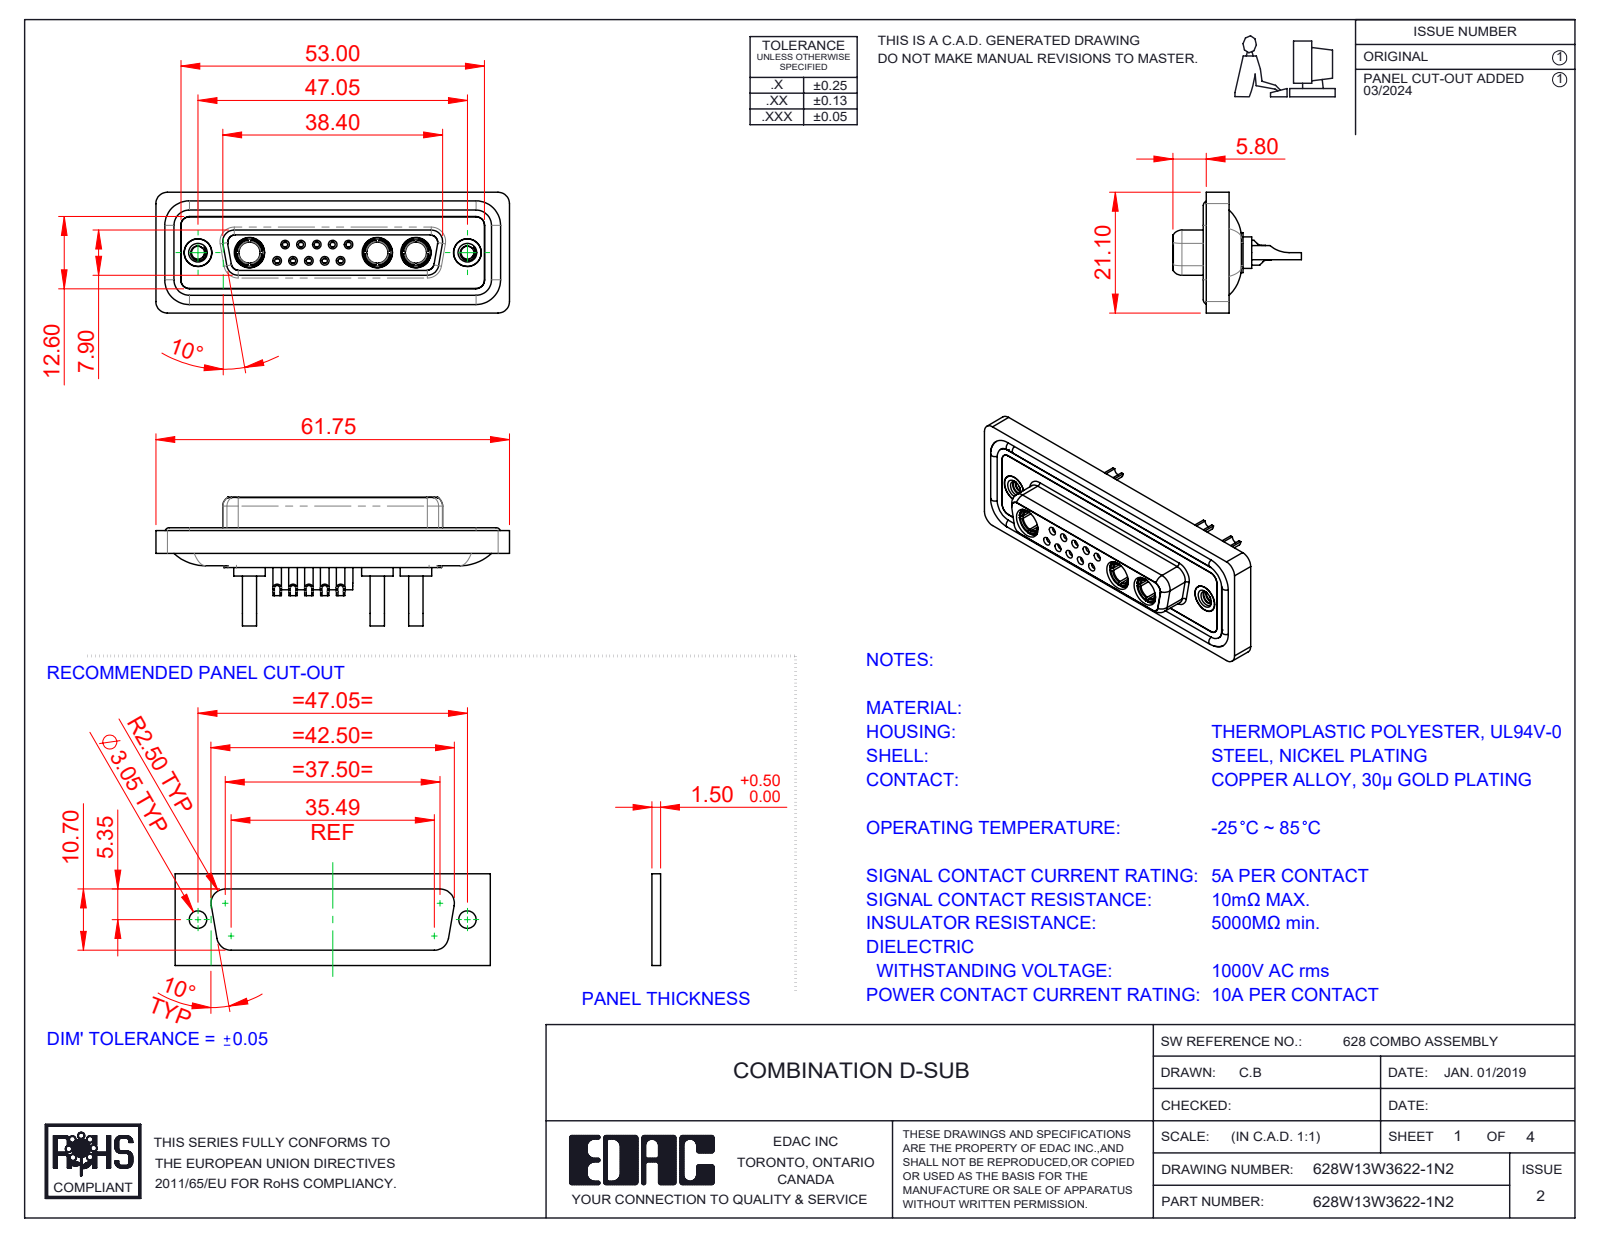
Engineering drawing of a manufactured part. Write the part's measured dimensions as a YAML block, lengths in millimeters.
part_name: "628Combo Shell Front_25 Contacts; 628W13W3622-1N2; 628Combo Housing_13W3; 628Combo Contact Row 1_22 (+5 more)"
step_written_by: "SolidWorks 2023 (CONFIG_CONTROL_DESIGN)"
units: millimeters
bodies: {solids: 23, faces: 1173, planar: 368, cylindrical: 476, other: 329}
overall_size: [61.75, 22.45, 21.1]
volume: 8285
surface_area: 13957
round_holes:
  - {diameter: 0.9, count: 10}
  - {diameter: 1, count: 10}
  - {diameter: 1.1, count: 10}
  - {diameter: 1.5, count: 10}
  - {diameter: 2, count: 10}
  - {diameter: 1.6, count: 5}
  - {diameter: 1.7, count: 5}
  - {diameter: 4.85, count: 5}
  - {diameter: 1.7, count: 3}
  - {diameter: 3.7, count: 3}
  - {diameter: 5.3, count: 3}
  - {diameter: 2.26, count: 2}
round_bosses_or_shafts:
  - {diameter: 2.2, count: 10}
  - {diameter: 1.6, count: 9}
  - {diameter: 5.5, count: 3}
  - {diameter: 5.2, count: 3}
  - {diameter: 4.96, count: 3}
  - {diameter: 4.75, count: 3}
  - {diameter: 3.75, count: 3}
  - {diameter: 2.5, count: 3}
partial_cylinders:
  - {radius: 1.5, count: 22}
  - {radius: 2, count: 18}
  - {radius: 1.35, count: 8}
  - {radius: 1.6, count: 8}
  - {radius: 1, count: 6}
  - {radius: 0.25, count: 4}
  - {radius: 0.5, count: 4}
  - {radius: 0.6, count: 4}
face_to_face_distances: [0.4, 1.8, 7.45, 5.65, 0.5, 6.6, 7.05, 1.6, 2.9, 1.1]
hole_center_spacings: [3.16, 2.77, 5.03, 5.04, 5.54, 8.31, 7.49, 2.76]
